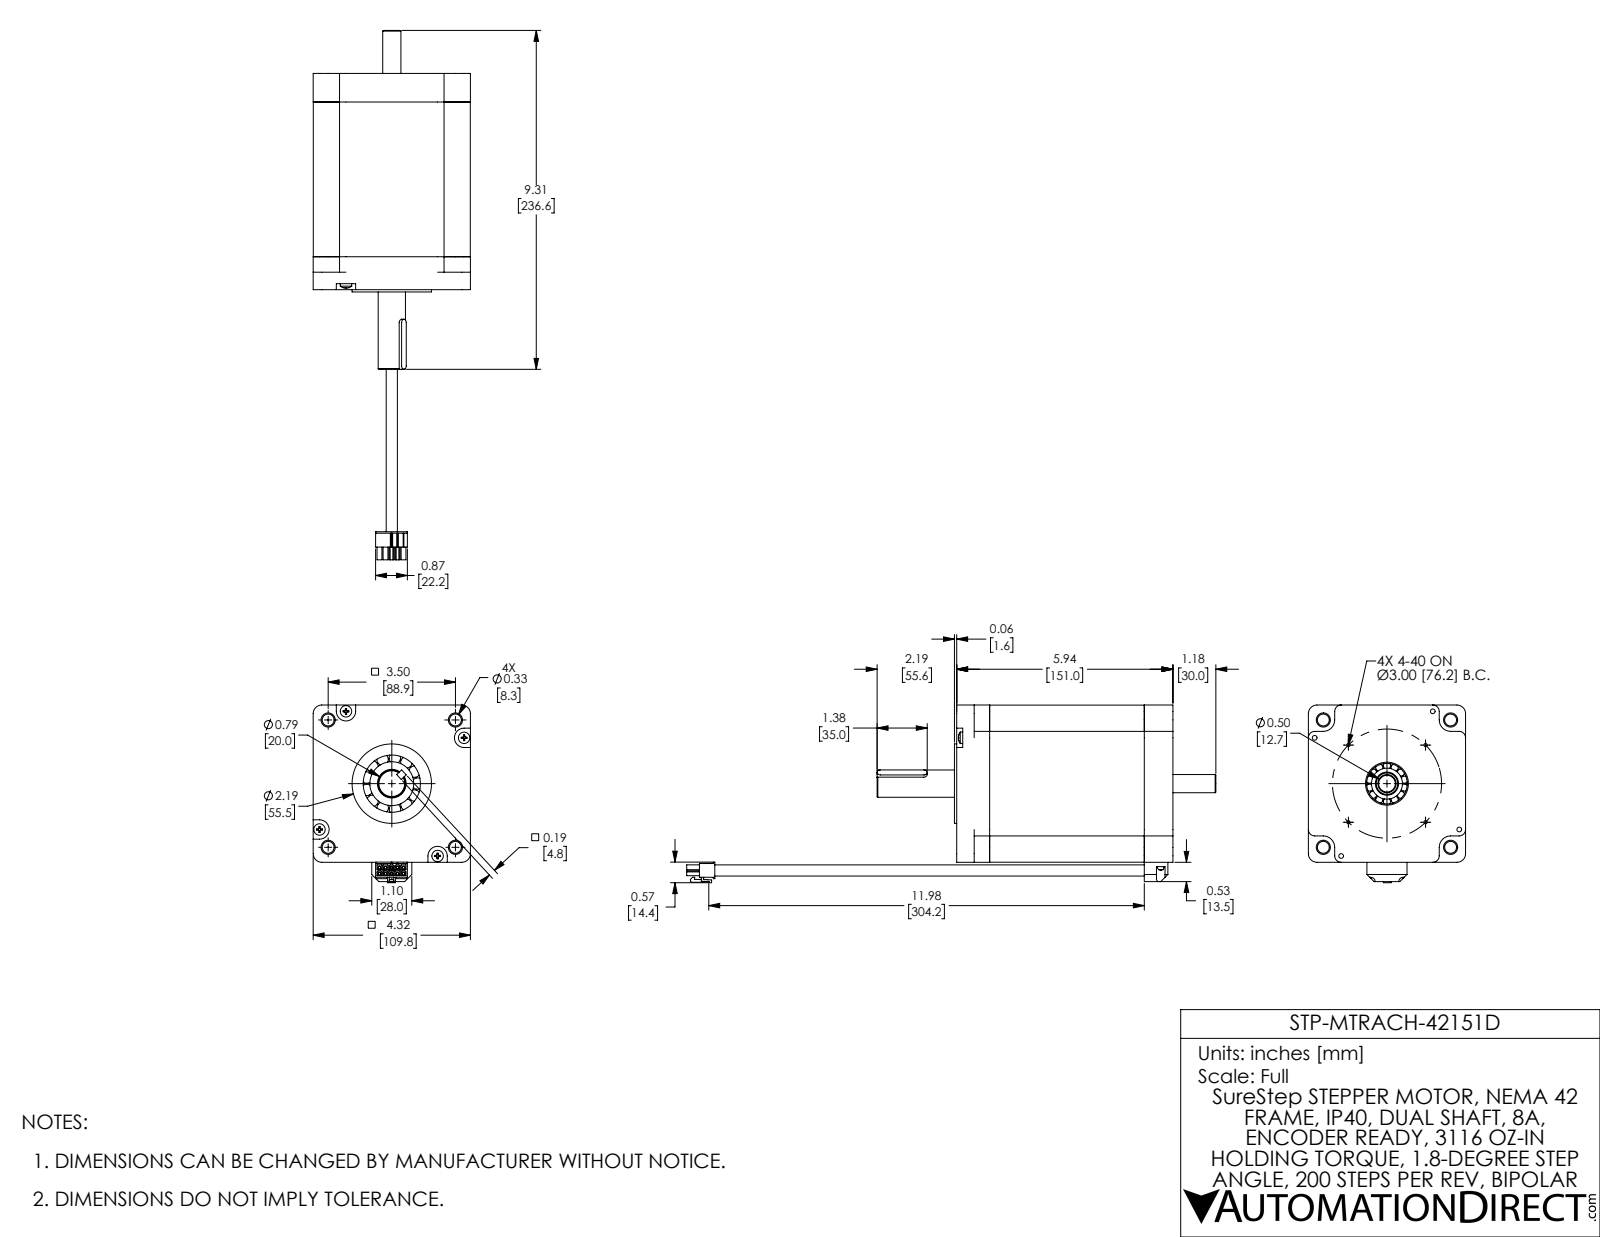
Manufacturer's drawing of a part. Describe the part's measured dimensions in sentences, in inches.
The part is named "STP-MTRAC-42151D". Its 3-D file was written by "SolidWorks 2017 (AUTOMOTIVE_DESIGN)". It is 13 solids with 1002 faces: 603 planar, 207 cylindrical and 192 other. Overall it measures 14.551 by 4.884 by 4.323 inches. Its volume is 50.93 cubic inches and its surface area 356.2 square inches. Round holes: 8 of diameter 0.177, 6 of diameter 0.13, 4 of diameter 0.181, 4 of diameter 0.327, 1 of diameter 0.591, 1 of diameter 0.787, 1 of diameter 1.116, 1 of diameter 1.181, 1 of diameter 1.378, 1 of diameter 1.575, 1 of diameter 1.627, 1 of diameter 2.047. Round bosses or shafts: 4 of diameter 0.315, 4 of diameter 0.157, 2 of diameter 0.177, 1 of diameter 2.579, 1 of diameter 2.559, 1 of diameter 2.186, 1 of diameter 1.207, 1 of diameter 1. Partial cylindrical surfaces (rounded edges, fillets, slot ends): 22 of radius 0.012, 16 of radius 0.177, 6 of radius 0.01, 4 of radius 0.236, 4 of radius 0.266, 4 of radius 0.315, 2 of radius 0.094, 2 of radius 0.118. The main face-to-face distances are 4.319, 4.321, 0.669, 5.945, 4.862, 0.787, 5.157, 4.252, 5.039, 0.906. The hole center spacings are 0.545, 2.354, 3.019, 3.329, 3.77, 4.799, 1.03, 2.475.
